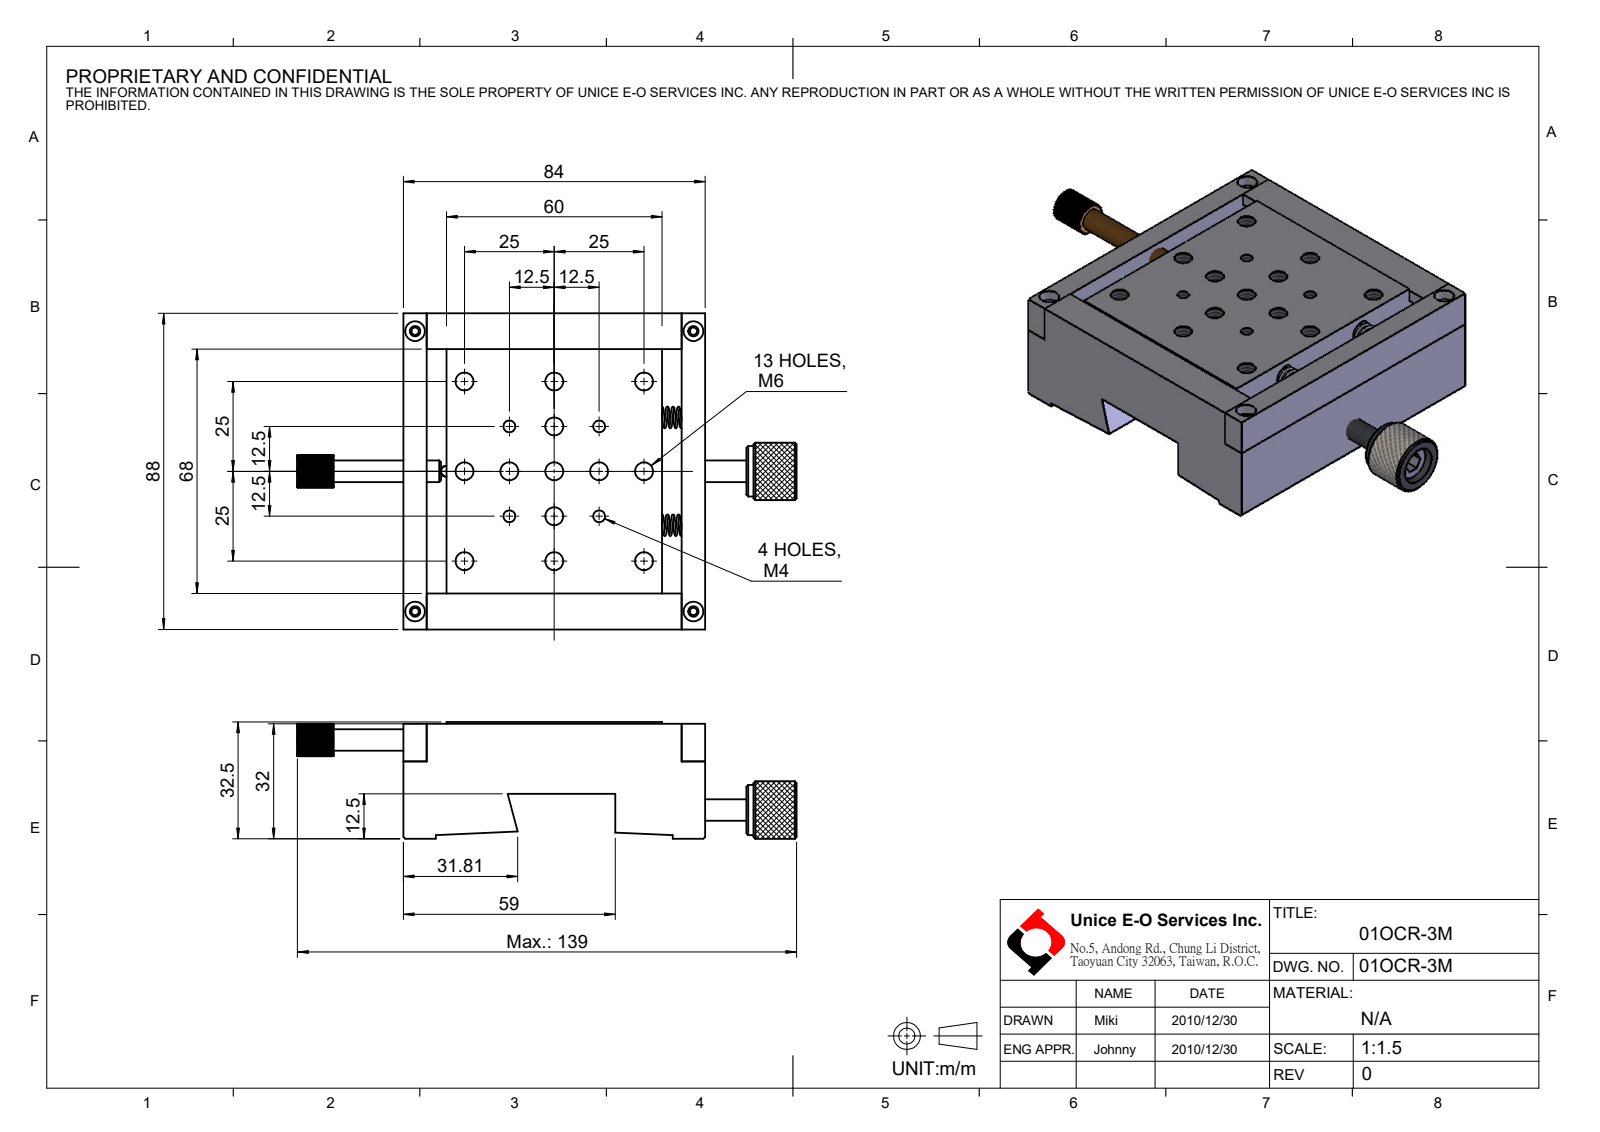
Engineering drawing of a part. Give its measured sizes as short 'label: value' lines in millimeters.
name: 01OCR-3M
written by: SolidWorks 2016 (CONFIG_CONTROL_DESIGN)
unit: mm
bodies: 11 solids, 388 faces (204 planar, 147 cylindrical, 37 other)
size: 139 × 88 × 32.5
volume: 192 275 mm³; area: 54 495 mm²
holes: 15× ⌀5, 4× ⌀2.05, 4× ⌀2.9, 4× ⌀3.3, 4× ⌀5.5, 2× ⌀6.3, 1× ⌀2.5, 1× ⌀10.5
bosses: 2× ⌀6, 1× ⌀16, 1× ⌀14, 1× ⌀10, 1× ⌀4
rounds: 1× R4.5
face distances: 10, 0.5, 10.5, 9.5, 6.5, 84, 20, 5, 19.5, 9
hole spacings: 27.95, 17.68, 25, 12.5, 39.53, 35.36, 45.07, 55.9
